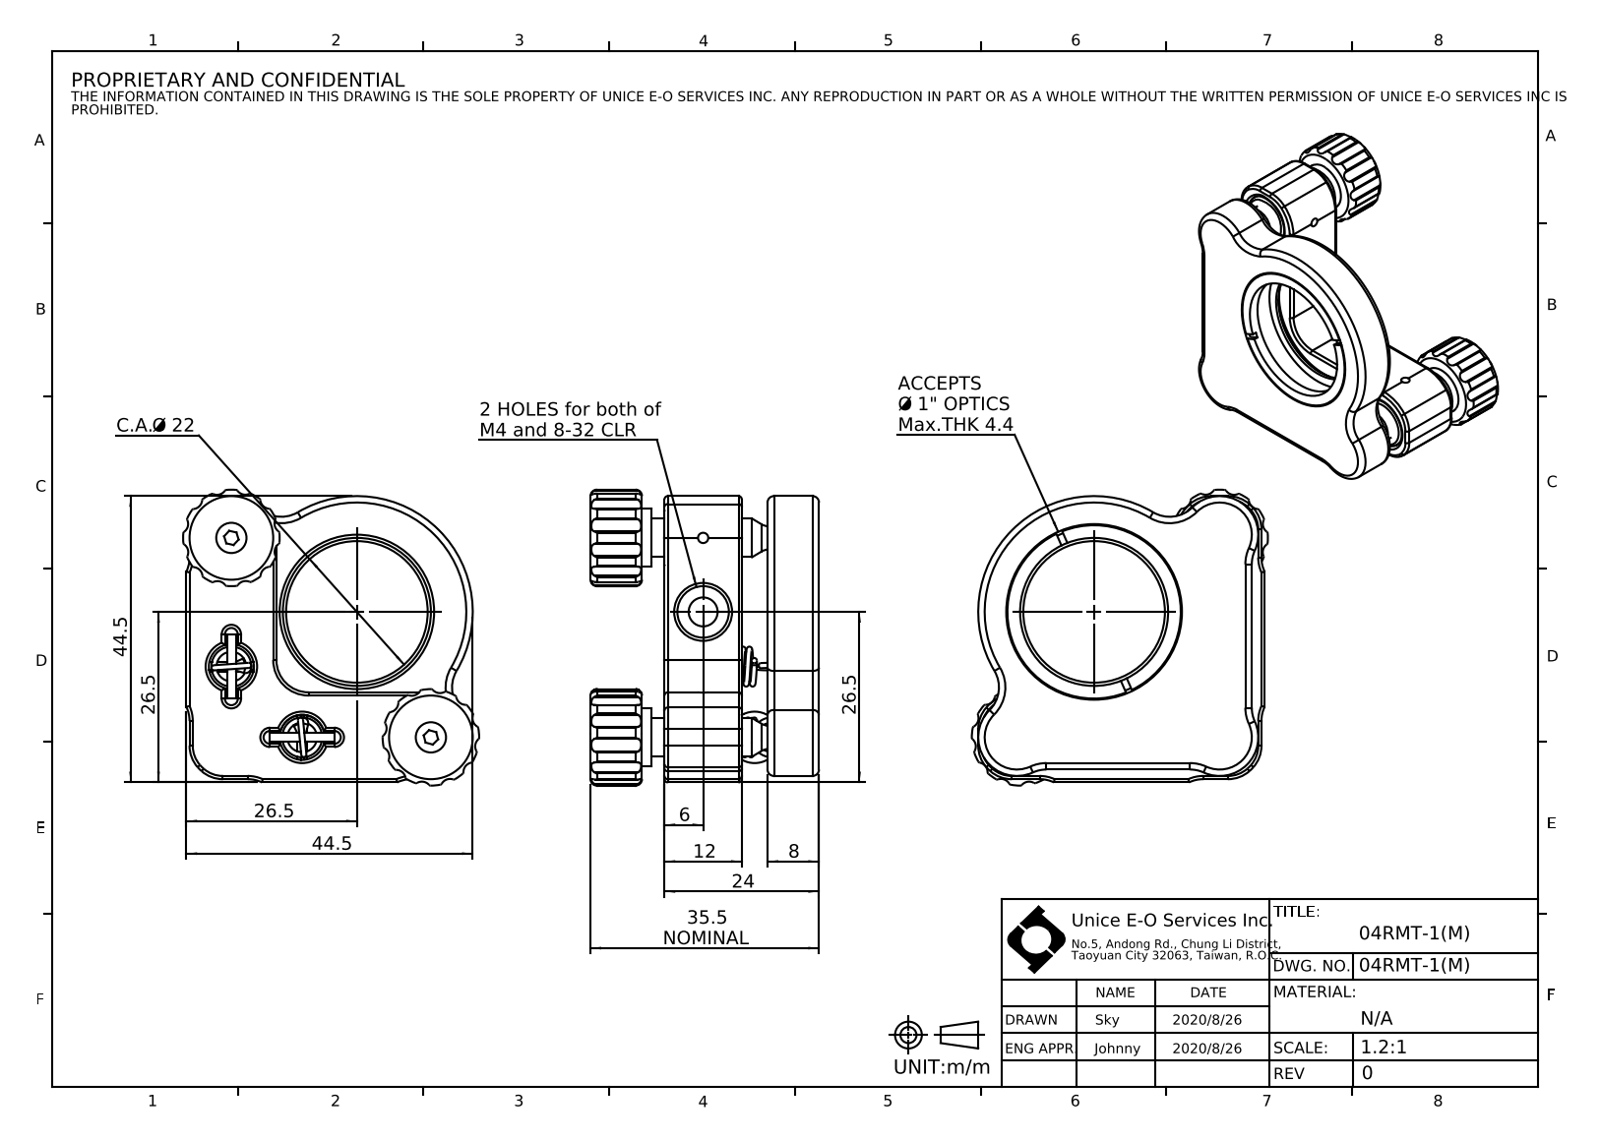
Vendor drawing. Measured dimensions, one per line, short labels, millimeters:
name: 04RMT-1(M)
written by: SolidWorks 2016 (CONFIG_CONTROL_DESIGN)
unit: mm
bodies: 0 solids, 446 faces (65 planar, 245 cylindrical, 136 other)
size: 46 × 46 × 35.5
holes: 4× ⌀1.1, 2× ⌀1.6, 2× ⌀1.7, 2× ⌀4.5, 2× ⌀4.7, 2× ⌀7, 2× ⌀8, 2× ⌀9.5, 1× ⌀6, 1× ⌀22, 1× ⌀23, 1× ⌀26.3
bosses: 6× ⌀1.5, 2× ⌀9.45, 2× ⌀9, 1× ⌀26.93, 1× ⌀6
rounds: 48× R0.3, 25× R1.5, 20× R0.5, 19× R5, 8× R1, 4× R0.75, 3× R6, 3× R7
face distances: 12, 8, 24, 4, 16, 2, 14, 27.5, 5, 1.5
hole spacings: 11.5, 17.24, 19.96, 20, 21.27, 22.17, 22.64, 25
